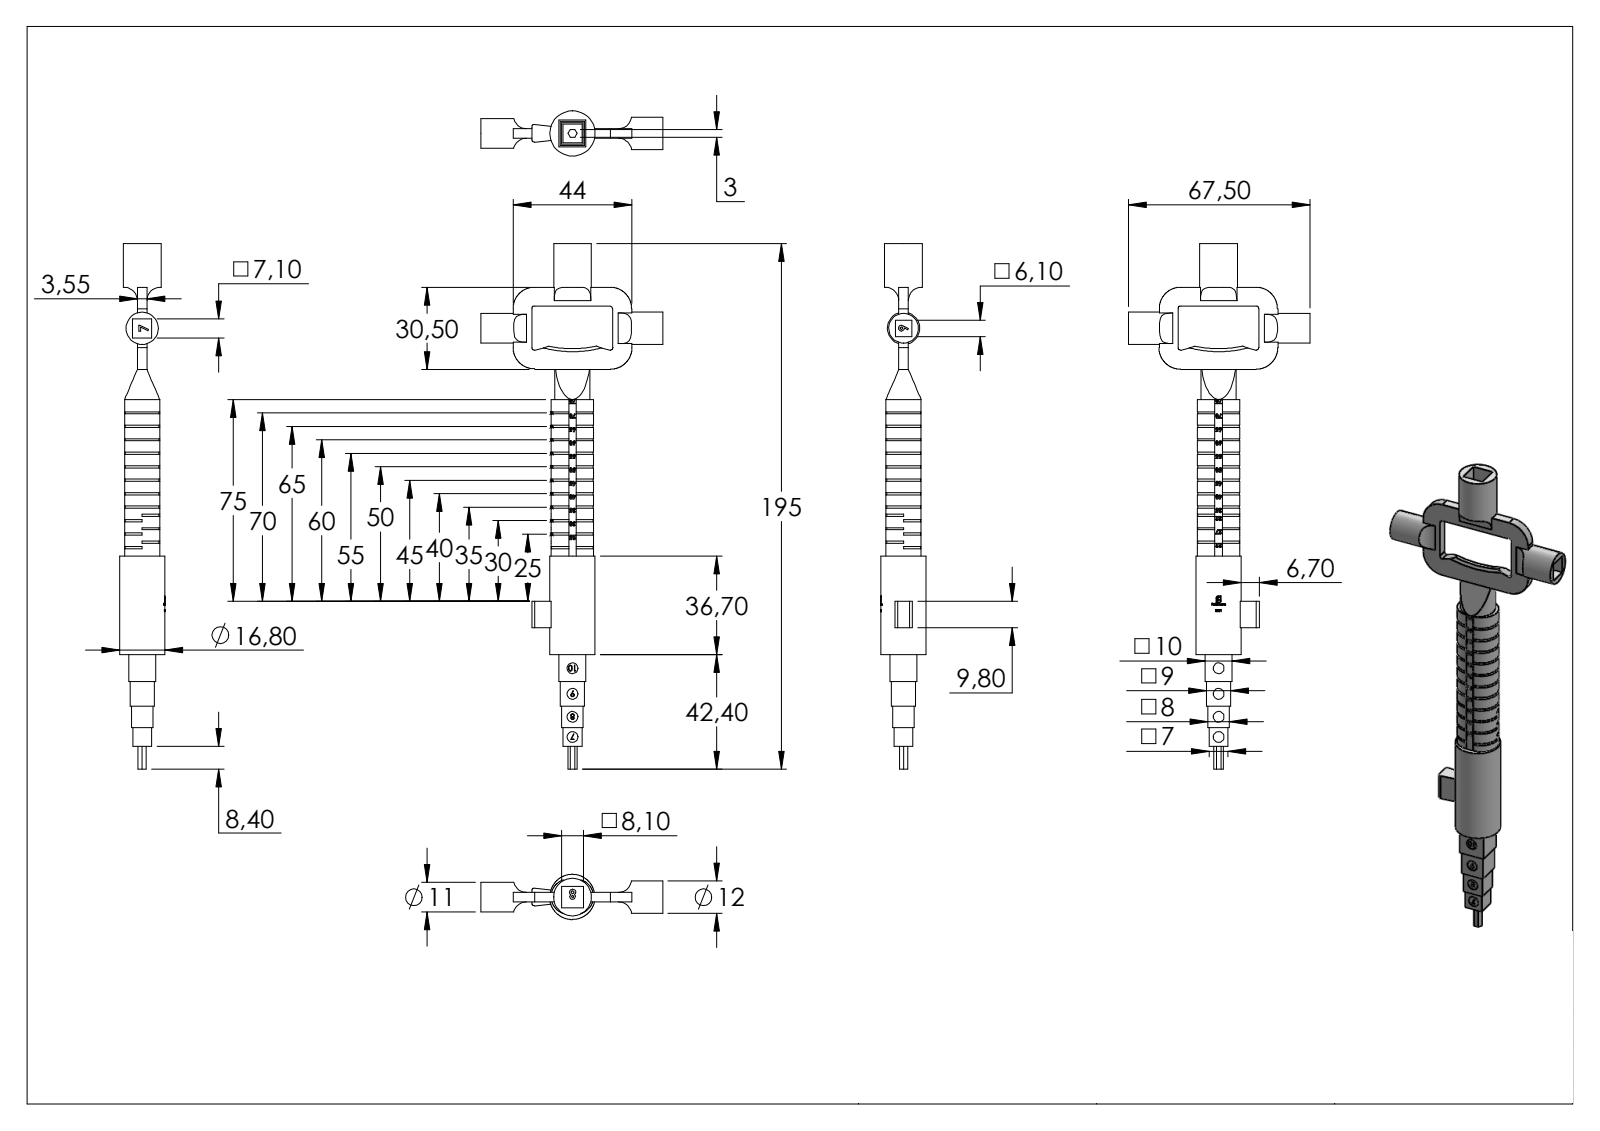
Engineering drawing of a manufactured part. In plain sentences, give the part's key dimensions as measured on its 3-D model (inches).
The part is named "8091". Its 3-D file was written by "SolidWorks 2018 (CONFIG_CONTROL_DESIGN)". It is 1 solid with 1035 faces: 553 planar, 97 cylindrical and 385 other. Overall it measures 7.677 by 2.657 by 0.661 inches. Its volume is 1.755 cubic inches and its surface area 18.91 square inches. Round holes: 4 of diameter 0.157. Round bosses or shafts: 1 of diameter 0.661, 1 of diameter 0.551, 1 of diameter 0.512, 1 of diameter 0.472, 1 of diameter 0.433. Partial cylindrical surfaces (rounded edges, fillets, slot ends): 6 of radius 0.039, 6 of radius 0.197, 4 of radius 0.315, 2 of radius 0.248, 2 of radius 0.256, 1 of radius 1.614. The main face-to-face distances are 0.02, 0.139, 0.354, 0.037, 0.039, 0.317, 0.018, 0.394, 0.337, 0.335. The hole center spacings are 0.295, 0.335, 0.374, 0.63, 0.709, 1.004.
